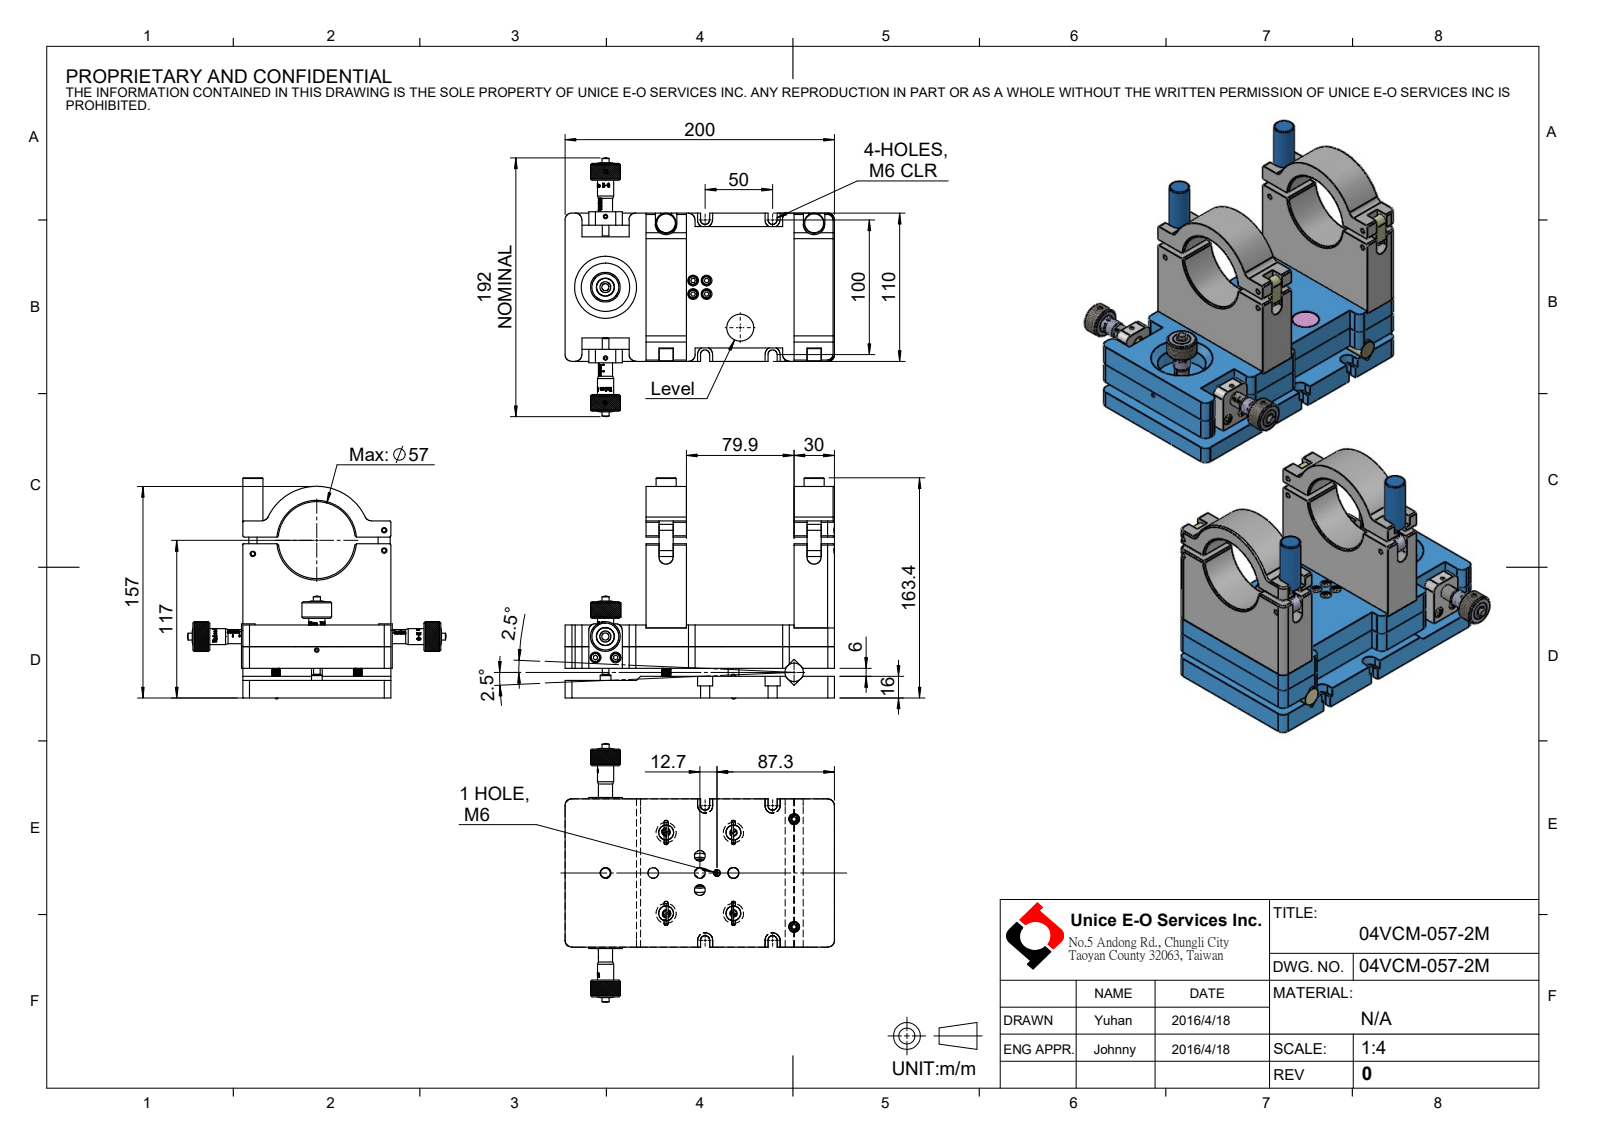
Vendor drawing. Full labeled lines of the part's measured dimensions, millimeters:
Part name (STEP PRODUCT): 04VCM-057-2M
STEP written by: SolidWorks 2021 (CONFIG_CONTROL_DESIGN)
Units: millimetres
Bodies: 0 solids, 722 faces (326 planar, 279 cylindrical, 117 other)
Overall size (bounding box): 200 × 192 × 164.25
Round holes (diameter × count): ⌀8 ×9, ⌀3.3 ×6, ⌀7.94 ×4, ⌀11 ×4, ⌀4 ×3, ⌀1.2 ×2, ⌀13.3 ×2, ⌀5.11 ×1, ⌀20 ×1, ⌀36 ×1, ⌀57.2 ×1
Round bosses / shafts (diameter × count): ⌀13 ×3, ⌀22 ×2, ⌀15 ×2, ⌀12 ×2, ⌀10.5 ×2, ⌀6 ×2, ⌀5.2 ×2, ⌀1.6 ×2
Partial cylindrical surfaces — rounded edges, fillets, slot ends (radius × count): R5 ×20, R1 ×9, R1.5 ×8, R3.4 ×4, R5.6 ×4, R0.5 ×2, R4.5 ×2, R5.25 ×2
Main face-to-face distances: 16, 22, 38.1, 16.1, 38, 30, 109.89, 6, 22.1, 110
Hole centre spacings: 39.05, 9.18, 18.39, 46.1, 7.07, 10, 30.4, 32.02
